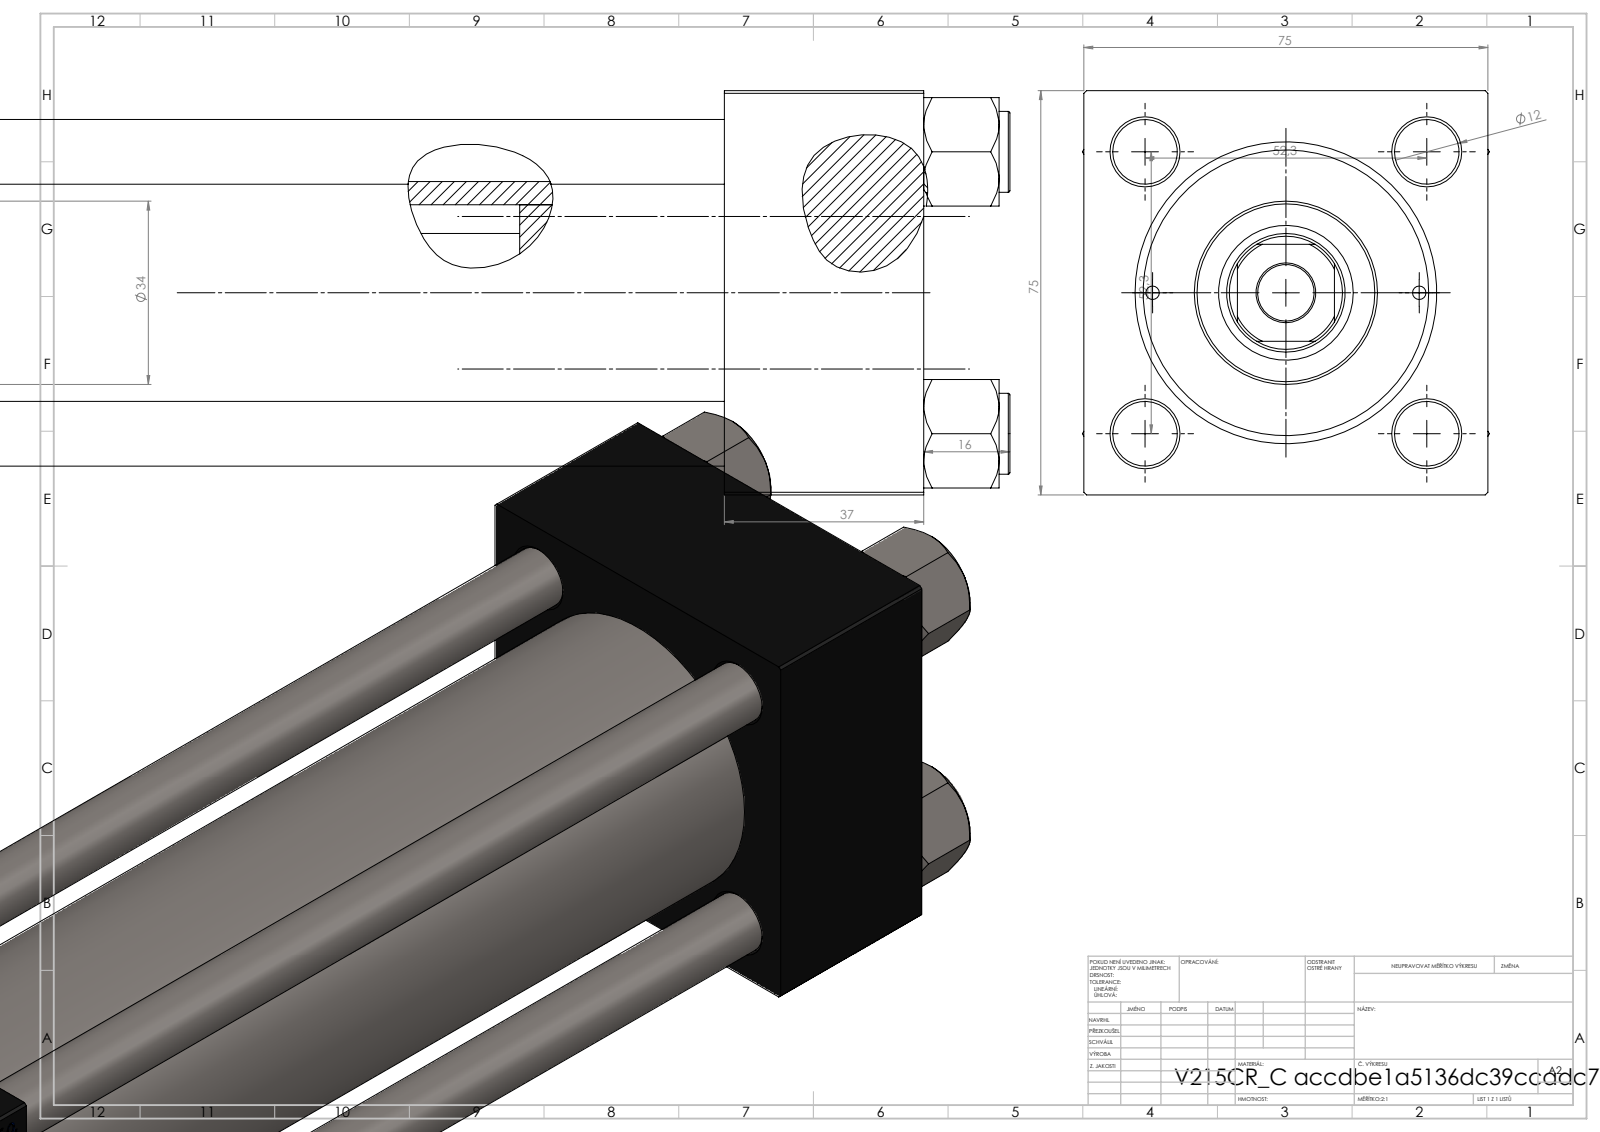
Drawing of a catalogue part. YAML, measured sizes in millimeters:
part_name: "V215CR_VCP_C; V215CR_C_Body; NUT_M5_C; V215CR_C_TYCINKA (+1 more)"
step_written_by: "SolidWorks 2019 (CONFIG_CONTROL_DESIGN)"
units: millimeters
bodies: {solids: 11, faces: 1155, planar: 528, cylindrical: 91, other: 536}
overall_size: [335, 75.54, 75]
volume: 843308
surface_area: 224774
round_holes:
  - {diameter: 12, count: 4}
  - {diameter: 2.5, count: 2}
  - {diameter: 7, count: 2}
  - {diameter: 20.96, count: 2}
  - {diameter: 30, count: 2}
  - {diameter: 10.5, count: 1}
  - {diameter: 22, count: 1}
  - {diameter: 25, count: 1}
  - {diameter: 41, count: 1}
  - {diameter: 50, count: 1}
  - {diameter: 53, count: 1}
round_bosses_or_shafts:
  - {diameter: 15, count: 4}
  - {diameter: 56, count: 1}
  - {diameter: 34, count: 1}
partial_cylinders:
  - {radius: 10.5, count: 1}
face_to_face_distances: [75, 37, 294, 257, 235, 198, 59, 265.3, 228.3, 30.3]
hole_center_spacings: [26.19, 36.98, 52.3, 57.22, 24.75, 73.96, 49.5, 233.5]
